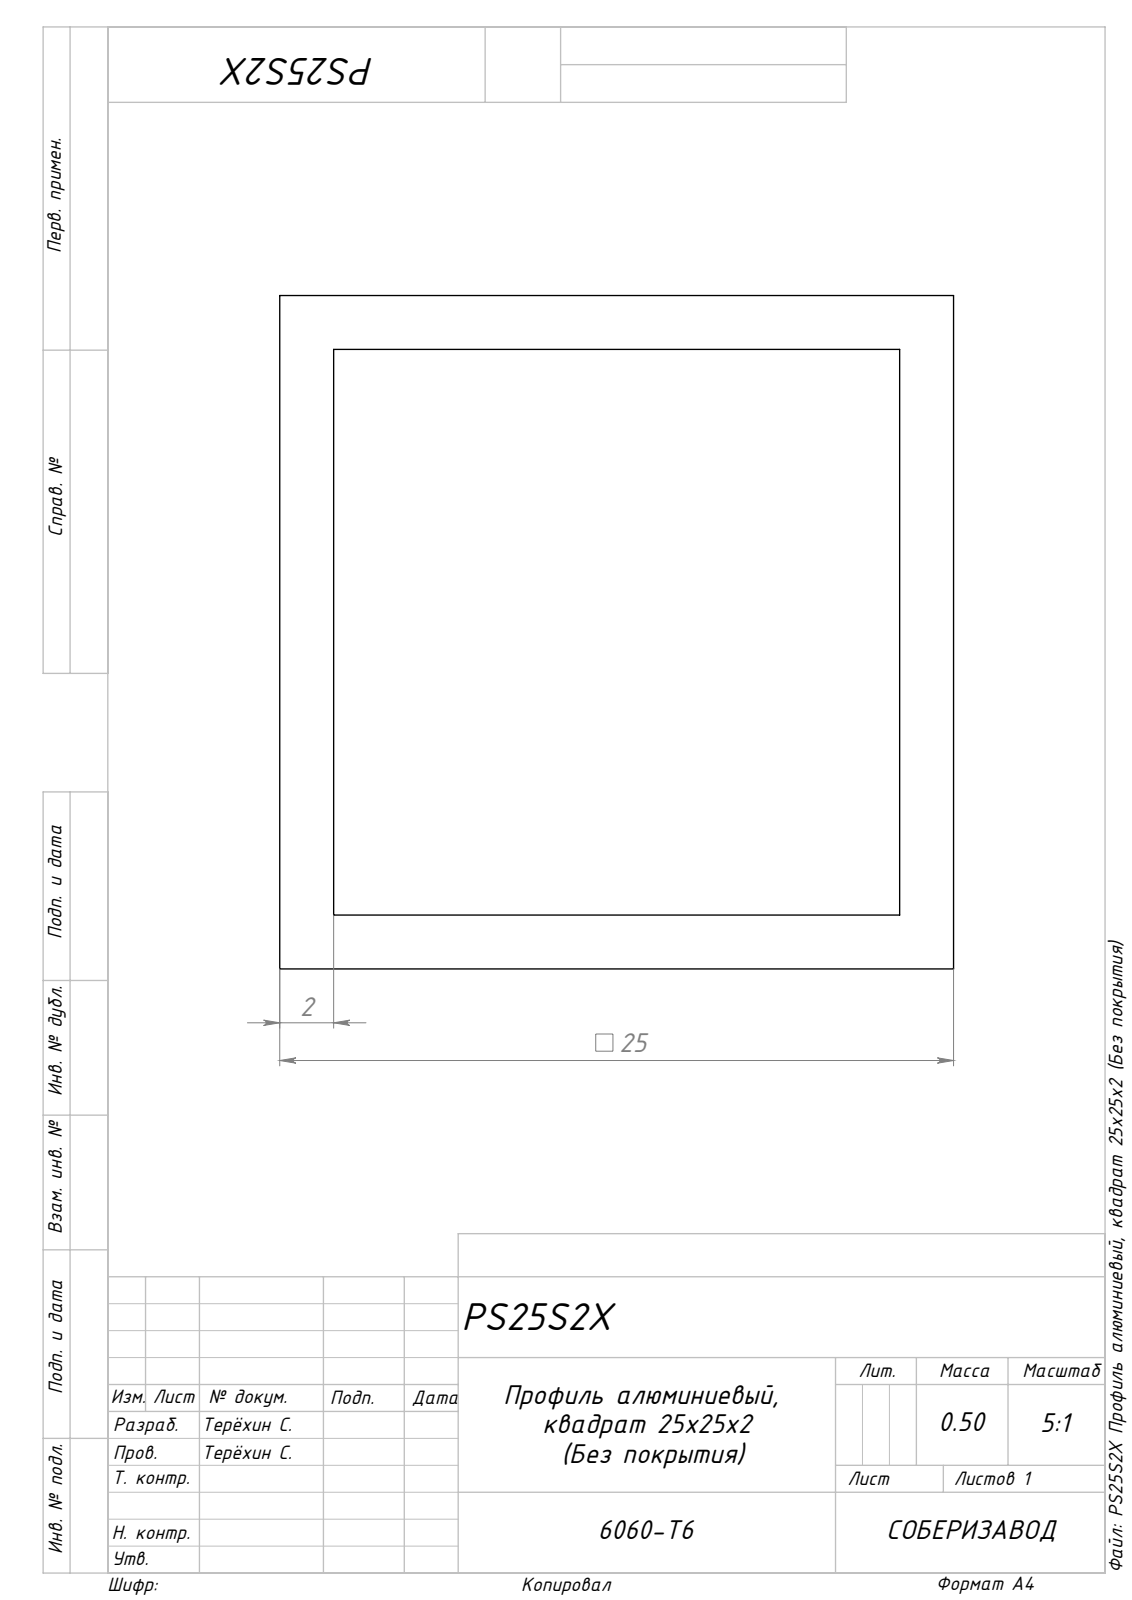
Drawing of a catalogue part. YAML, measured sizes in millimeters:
part_name: "PS25S2X Профиль алюминиевый, квадрат 25x25x2 (Без покрытия)_00; Сборка2"
step_written_by: "SolidWorks 2025 (AUTOMOTIVE_DESIGN)"
units: millimeters
bodies: {solids: 1, faces: 10, planar: 10, cylindrical: 0, other: 0}
overall_size: [1000, 25, 25]
volume: 184000
surface_area: 184368
face_to_face_distances: [2, 23, 25, 21, 1000]
